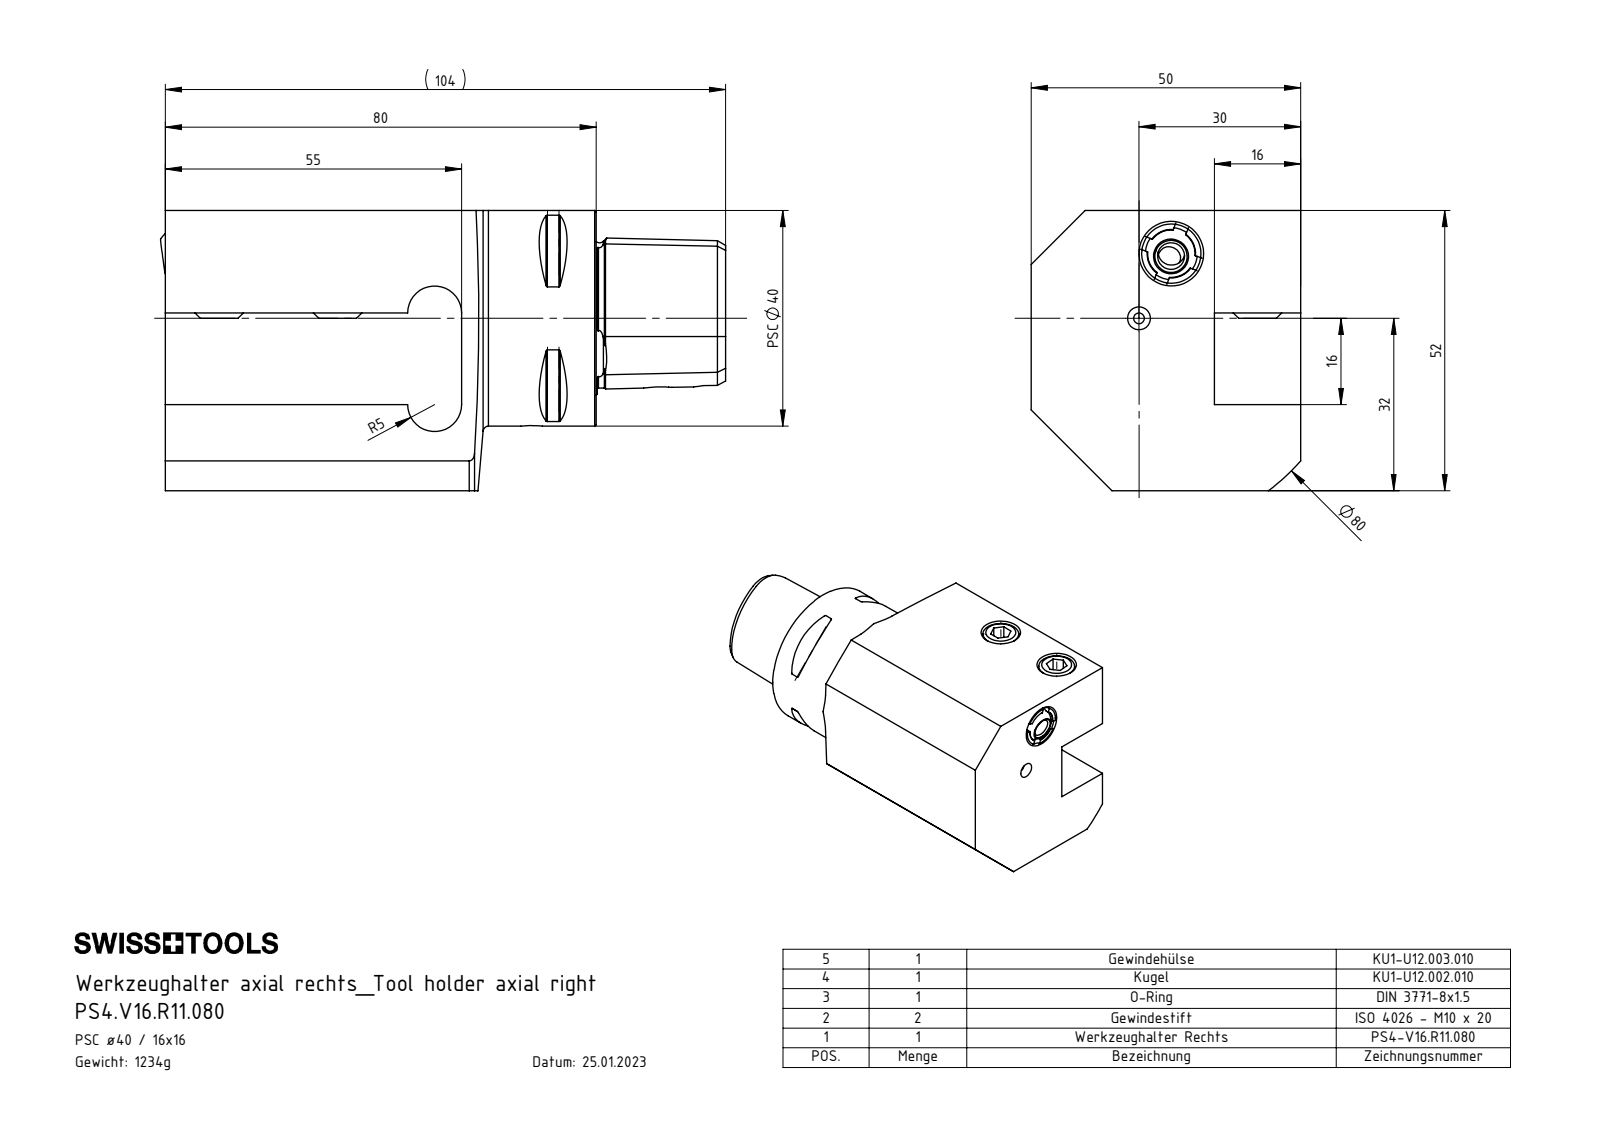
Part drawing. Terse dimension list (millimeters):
name: PS4.V16.R11.080; KU1-U12.003.010_B; DIN 3771 - 8x1.5; ISO 4026 - M10 x 20 (+2 more)
written by: SolidWorks 2017 (AUTOMOTIVE_DESIGN)
unit: mm
bodies: 6 solids, 252 faces (65 planar, 54 cylindrical, 133 other)
size: 104.89 × 52 × 50
volume: 157 212 mm³; area: 28 820 mm²
holes: 3× ⌀8.5, 1× ⌀2, 1× ⌀4, 1× ⌀4.2, 1× ⌀4.6, 1× ⌀5, 1× ⌀10, 1× ⌀11, 1× ⌀12.5, 1× ⌀18, 1× ⌀20
bosses: 2× ⌀10, 1× ⌀40, 1× ⌀12
rounds: 8× R0.3, 2× R5, 1× R3, 1× R4.4, 1× R40
face distances: 16, 52, 50, 34, 36, 33, 17, 19, 80, 25
hole spacings: 13.42, 22, 23.5, 42.19, 62.03, 63.44, 84.42
